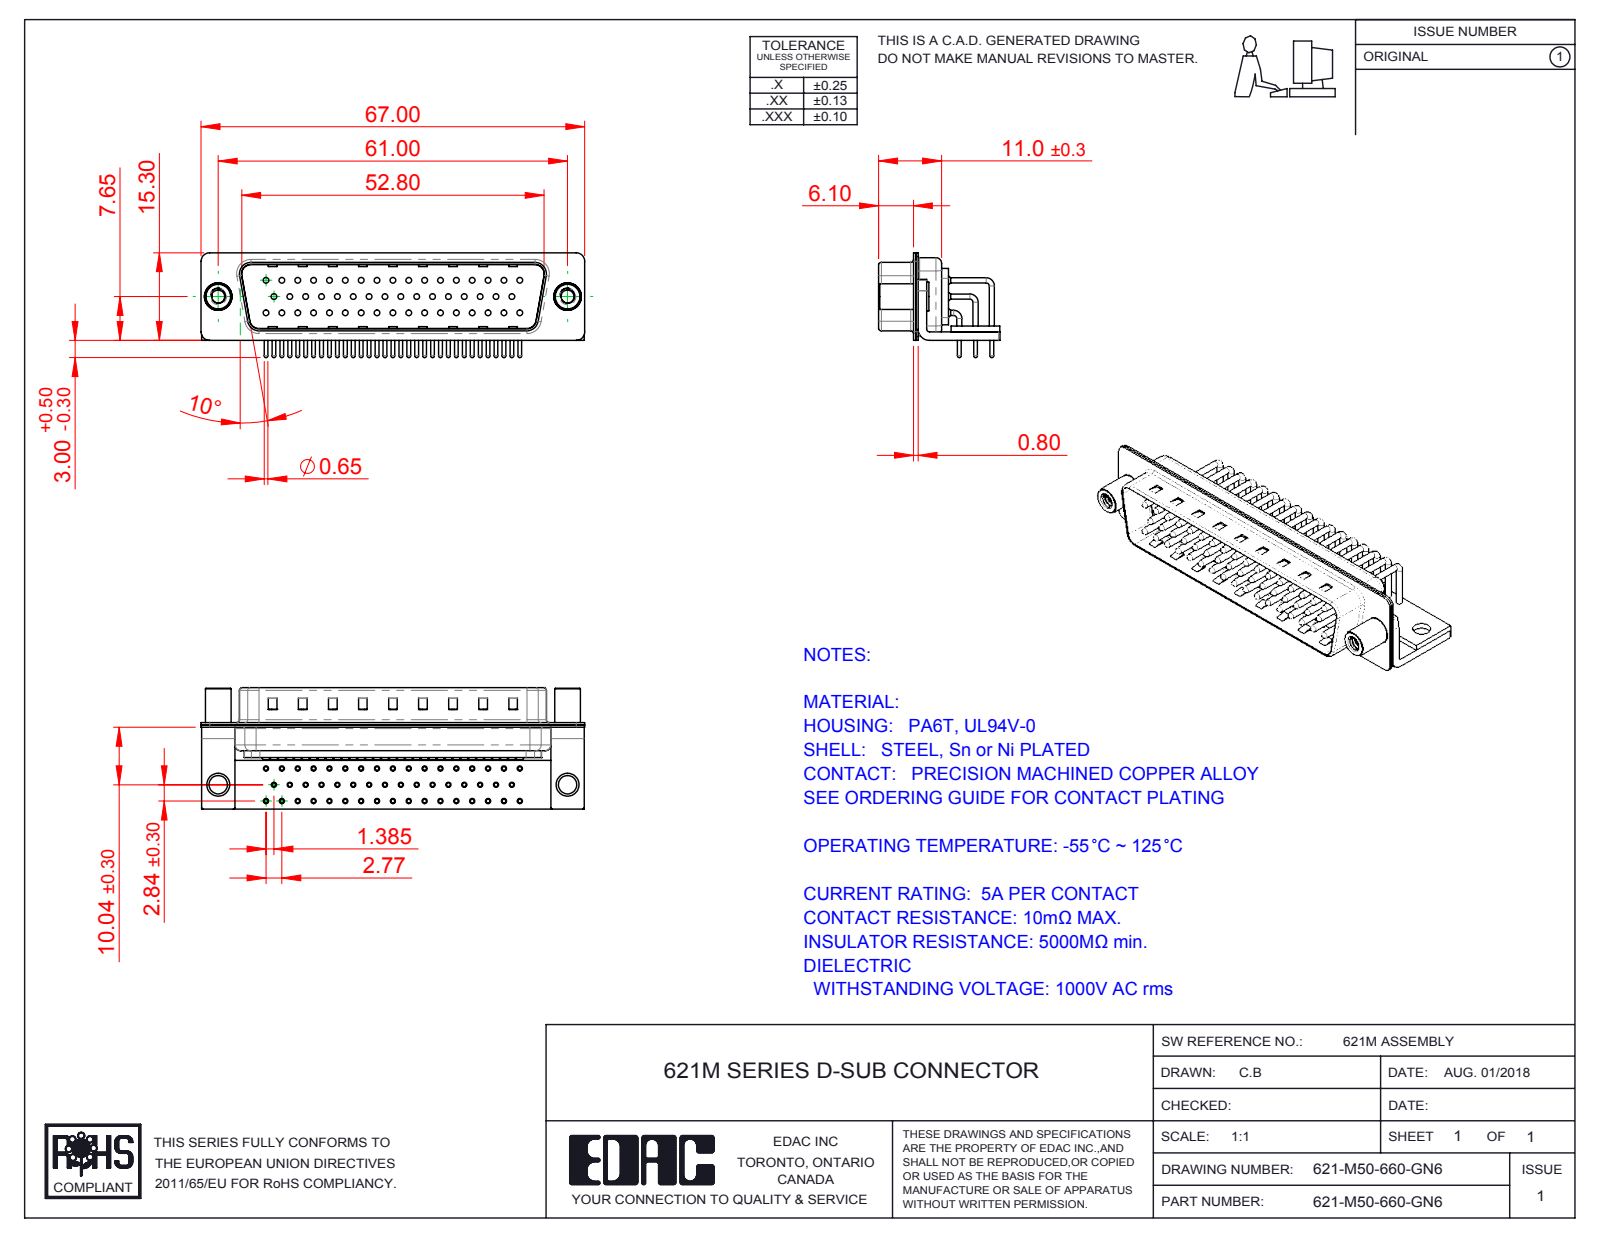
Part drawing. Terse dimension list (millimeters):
name: 621M Housing_50 Contacts; 621M Shell Front_50 Contacts; 621M Shell Rear_50 Contacts; 621M Contact Row 1_50 Contacts (+6 more)
written by: SolidWorks 2016 (CONFIG_CONTROL_DESIGN)
unit: mm
bodies: 58 solids, 6112 faces (3431 planar, 2105 cylindrical, 576 other)
size: 67 × 21.2 × 18.3
volume: 5 860 mm³; area: 14 877 mm²
holes: 50× ⌀0.9, 50× ⌀1, 50× ⌀1.7, 50× ⌀2, 2× ⌀2.26, 2× ⌀3.2, 2× ⌀4, 2× ⌀4.8
bosses: 58× ⌀0.9, 50× ⌀1.5, 50× ⌀0.65, 2× ⌀5, 2× ⌀4.9, 2× ⌀4.5
rounds: 50× R1.01, 16× R0.25, 16× R1.5, 13× R2, 9× R0.5, 8× R1.6, 4× R0.6, 4× R0.65
face distances: 0.4, 1, 11.55, 0.83, 1.5, 5.7, 0.43, 11.95, 1.9, 0.8
hole spacings: 2.77, 3.16, 5.54, 8.31, 11.08, 13.85, 16.62, 19.39
